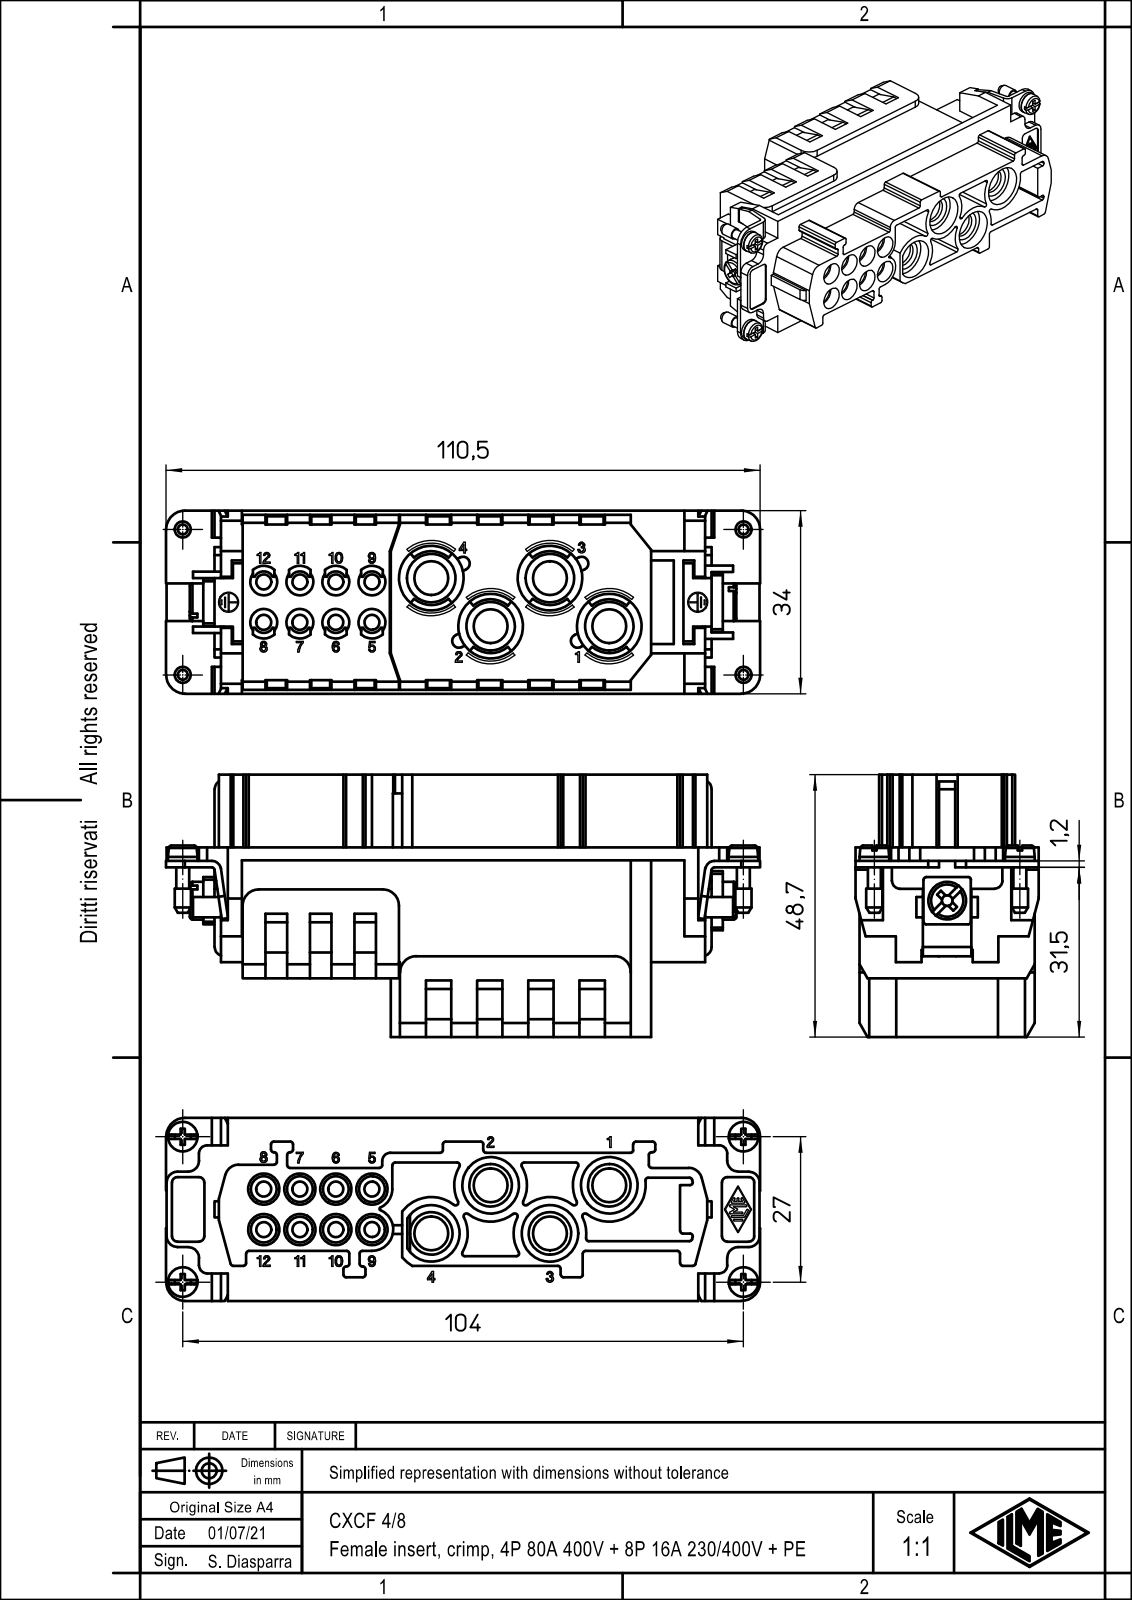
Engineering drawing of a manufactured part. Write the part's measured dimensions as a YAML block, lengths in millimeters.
part_name: "CXCF_4-8"
step_written_by: "Creo Elements/Direct Modeling 20.1B 02-Apr-2019 (C) Parametric Technology GmbH (AUTOMOTIVE_DESIGN)"
units: millimeters
bodies: {solids: 1, faces: 1735, planar: 1388, cylindrical: 295, other: 52}
overall_size: [110.2, 48.7, 34]
volume: 74574
surface_area: 36992
round_holes:
  - {diameter: 2.8, count: 8}
  - {diameter: 5, count: 8}
  - {diameter: 5.8, count: 8}
  - {diameter: 6.3, count: 4}
  - {diameter: 9, count: 4}
  - {diameter: 10.5, count: 4}
  - {diameter: 12, count: 4}
  - {diameter: 2, count: 1}
round_bosses_or_shafts:
  - {diameter: 5.5, count: 4}
  - {diameter: 3, count: 4}
  - {diameter: 2.4, count: 4}
  - {diameter: 7, count: 1}
partial_cylinders:
  - {radius: 0.5, count: 66}
  - {radius: 0.17, count: 15}
  - {radius: 3, count: 12}
  - {radius: 1, count: 8}
  - {radius: 1.95, count: 8}
  - {radius: 2, count: 8}
  - {radius: 1.5, count: 7}
  - {radius: 1.7, count: 6}
face_to_face_distances: [1.8, 30.7, 5.75, 24.95, 22.15, 8.55, 6.75, 23.95, 18.2, 28.9]
hole_center_spacings: [6.7, 10.06, 7.5, 13.4, 15.36, 14.15, 20.1, 21.45]
